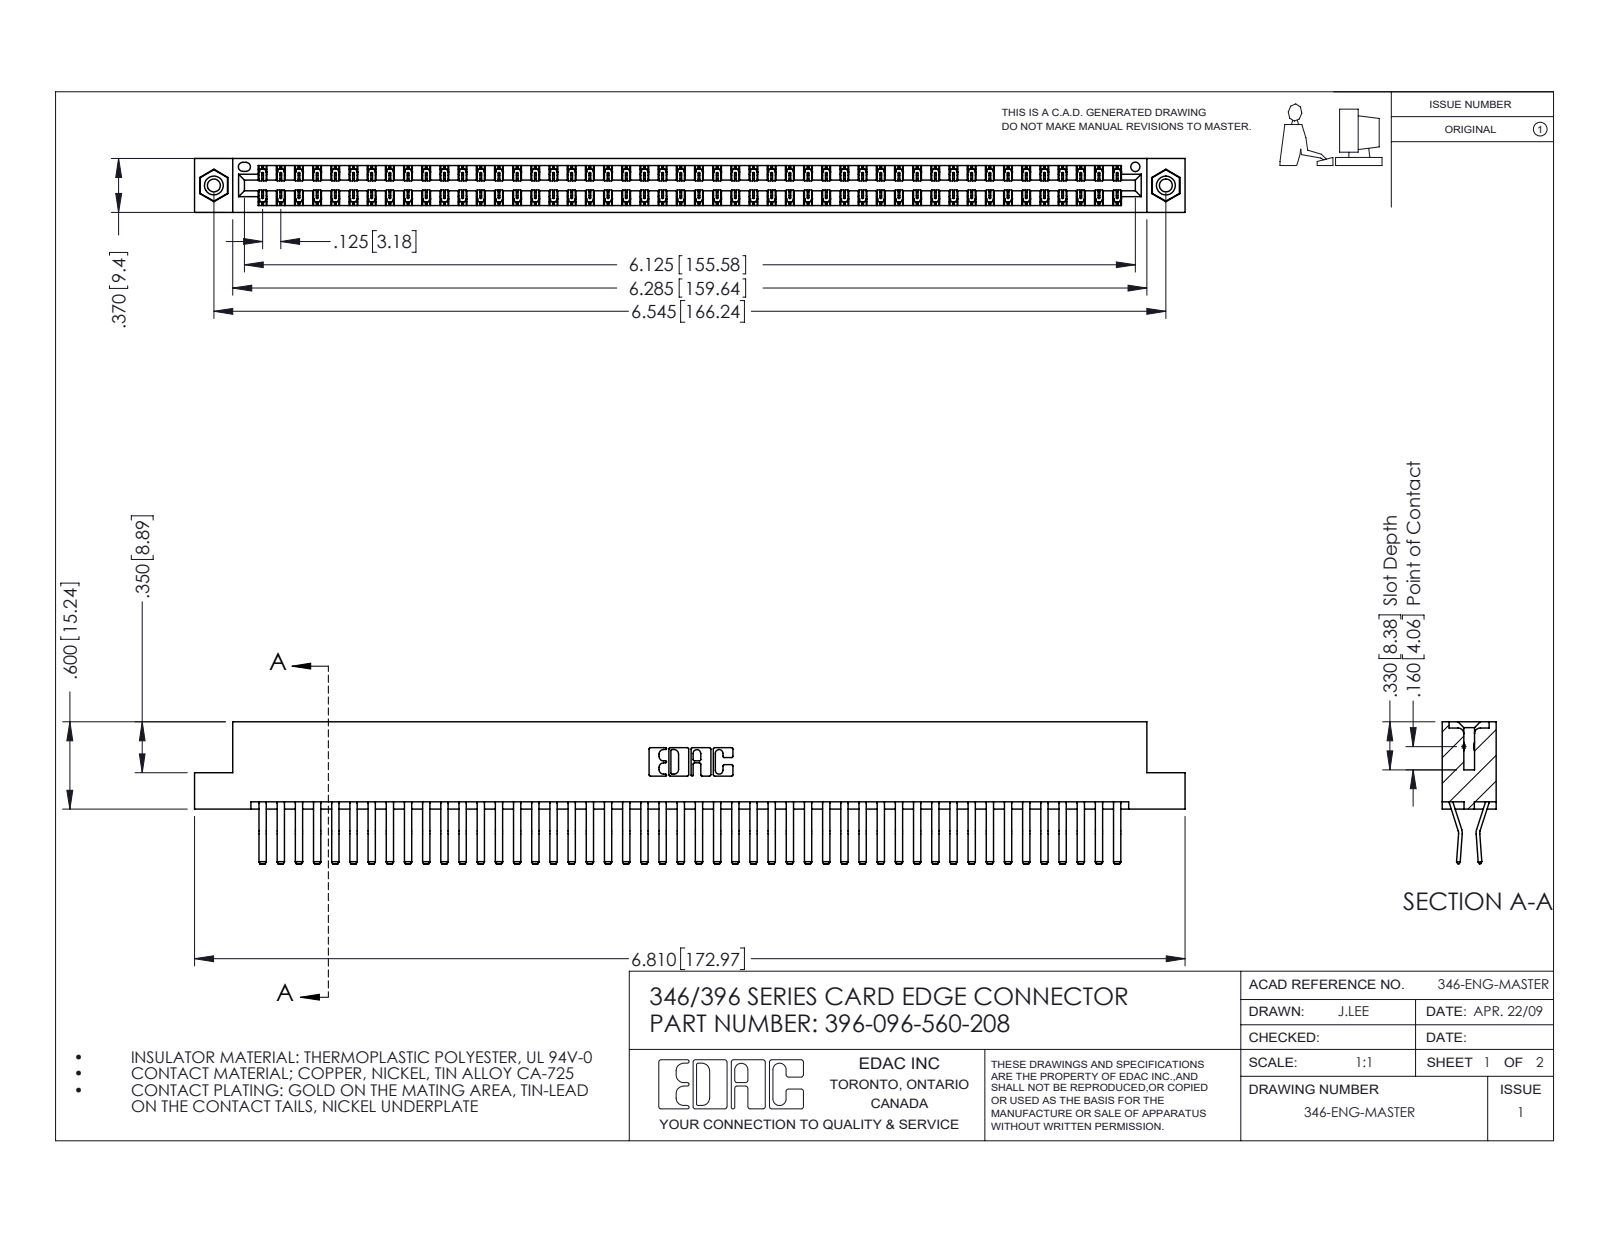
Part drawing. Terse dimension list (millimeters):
name: 345-250-001_345-250-003-102; 396-096-560-208; 346 Part_Flush Mounting Lugs - 0.156 Dia-TI; 345-292-001_560 Tail
written by: SolidWorks 2016 (CONFIG_CONTROL_DESIGN)
unit: mm
bodies: 99 solids, 5366 faces (3468 planar, 1882 cylindrical, 16 other)
size: 173 × 24.8 × 9.4
volume: 17 530 mm³; area: 25 900 mm²
holes: 2× ⌀2.3, 2× ⌀3.2, 2× ⌀4, 1× ⌀1.6
bosses: 2× ⌀3.9
rounds: 144× R0.2, 22× R0.3, 6× R0.2, 6× R0.8, 3× R0.7, 2× R0.3, 2× R0.4, 2× R0.6
face distances: 1.2, 8.2, 9.4, 0.6, 6.4, 1.8, 7.6, 7, 3.8, 5.6
hole spacings: 6.2, 160.9, 166.2
